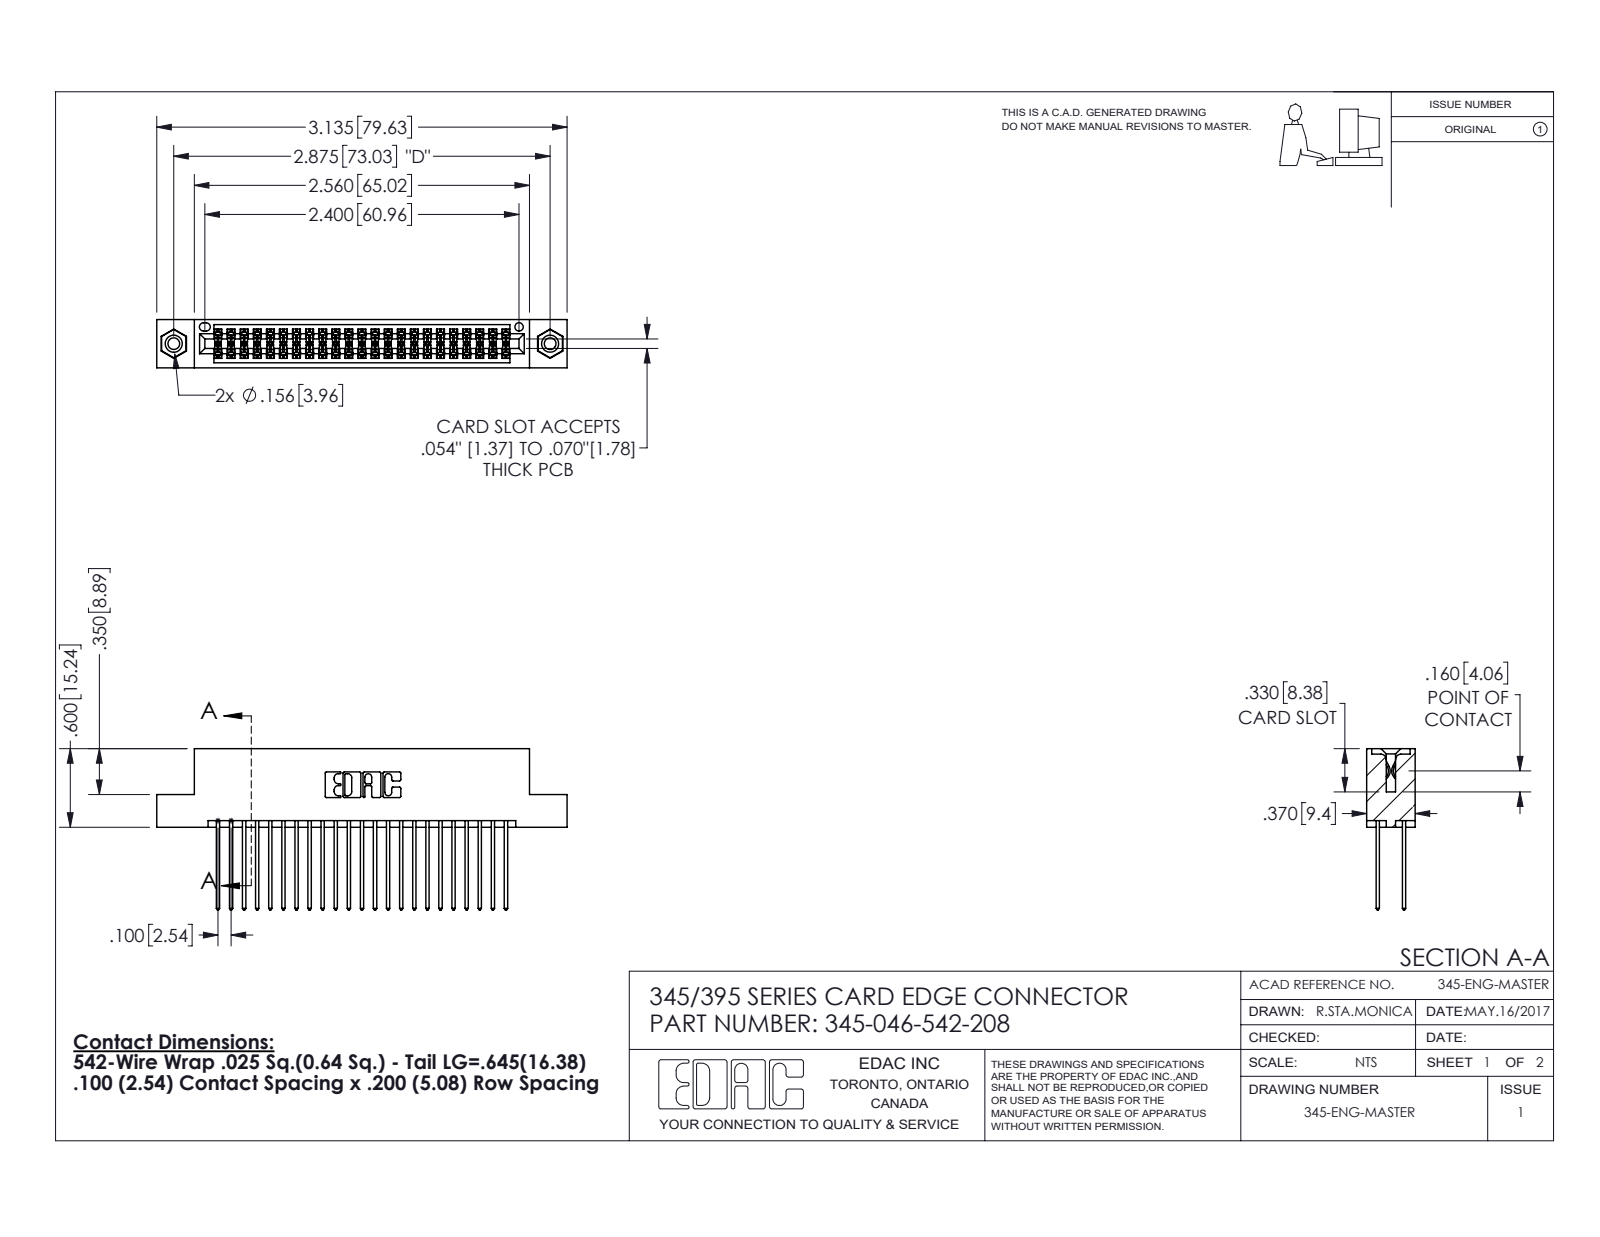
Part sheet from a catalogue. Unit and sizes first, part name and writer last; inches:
Units: inches
Overall size (bounding box): 3.135 × 1.232 × 0.37
Round holes (diameter × count): ⌀0.089 ×2, ⌀0.125 ×2, ⌀0.156 ×2, ⌀0.064 ×1
Round bosses / shafts (diameter × count): ⌀0.155 ×2
Partial cylindrical surfaces — rounded edges, fillets, slot ends (radius × count): R0.006 ×69, R0.01 ×46, R0.01 ×22, R0.007 ×6, R0.031 ×6, R0.026 ×3, R0.014 ×2, R0.019 ×2
Main face-to-face distances: 0.072, 0.298, 0.2, 0.098, 0.272, 0.025, 0.37, 0.225, 0.175, 0.149
Hole centre spacings: 0.27, 2.641, 2.875
Volume: 0.474 in³ · Surface area: 18.8 in²
Bodies: 49 solids, 2486 faces (1630 planar, 840 cylindrical, 16 other)
Part name (STEP PRODUCT): 345-292-001_345-293-142; 345 Part_Flush Mounting Lugs - 0.156 Dia-TI; 345-250-001_345-250-003-102; 345-046-542-208
STEP written by: SolidWorks 2016 (CONFIG_CONTROL_DESIGN)
